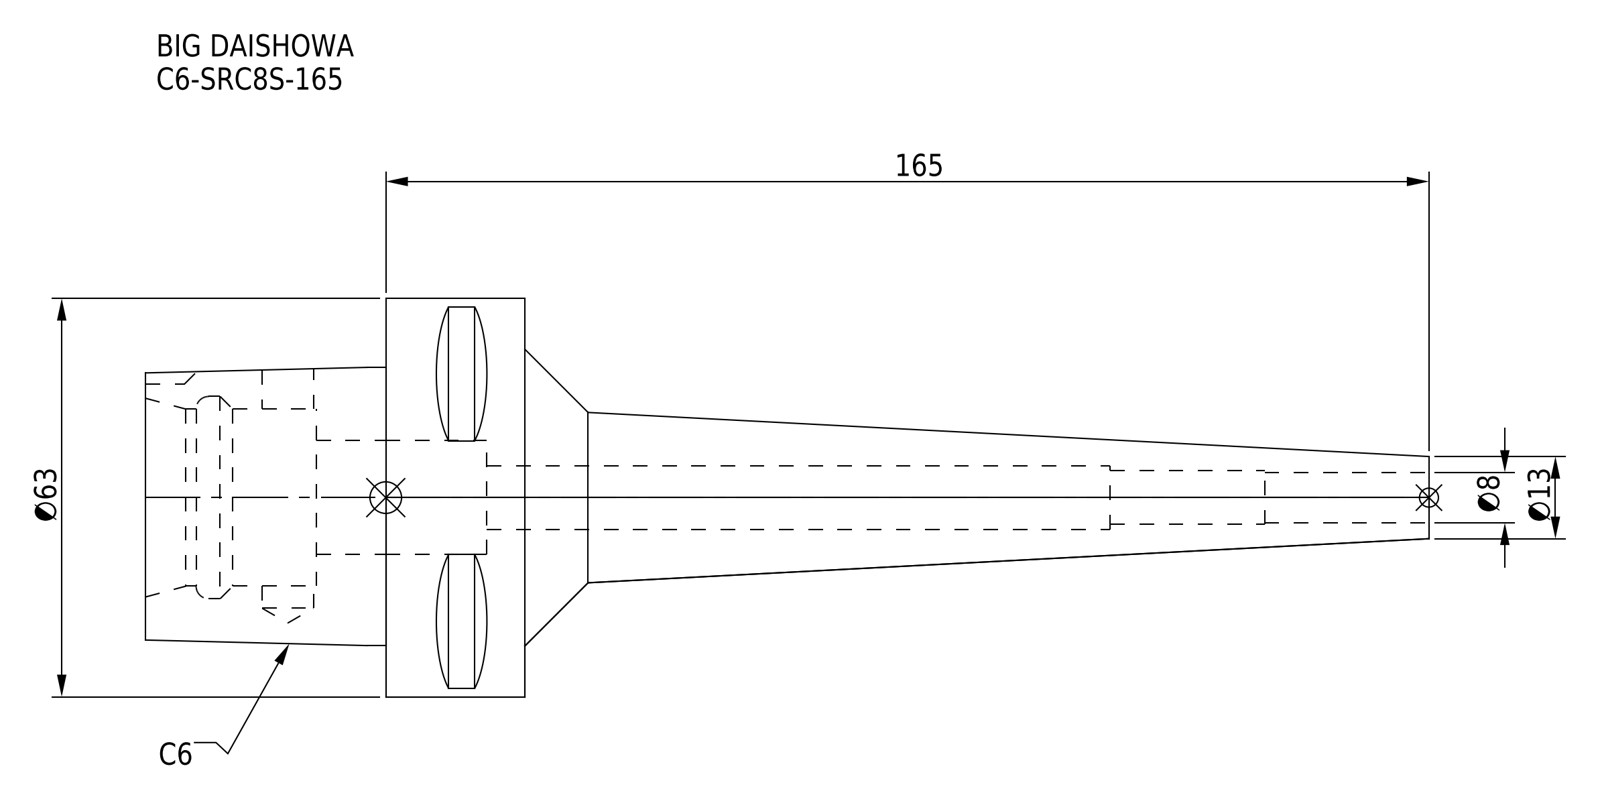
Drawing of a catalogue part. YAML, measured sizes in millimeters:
part_name: "C6-SRC8S-165"
step_written_by: "CREO PARAMETRIC BY PTC INC, 2016380 (AUTOMOTIVE_DESIGN)"
units: millimeters
bodies: {solids: 1, faces: 65, planar: 30, cylindrical: 21, other: 14}
overall_size: [203, 63, 63]
volume: 140479
surface_area: 32850
round_holes:
  - {diameter: 8, count: 1}
  - {diameter: 8.1, count: 1}
  - {diameter: 8.5, count: 1}
  - {diameter: 10, count: 1}
  - {diameter: 18, count: 1}
  - {diameter: 28, count: 1}
  - {diameter: 32, count: 1}
round_bosses_or_shafts:
  - {diameter: 63, count: 1}
partial_cylinders:
  - {radius: 5, count: 1}
face_to_face_distances: [22, 27, 60, 38, 33, 11, 24.89, 55.4, 6, 16]
